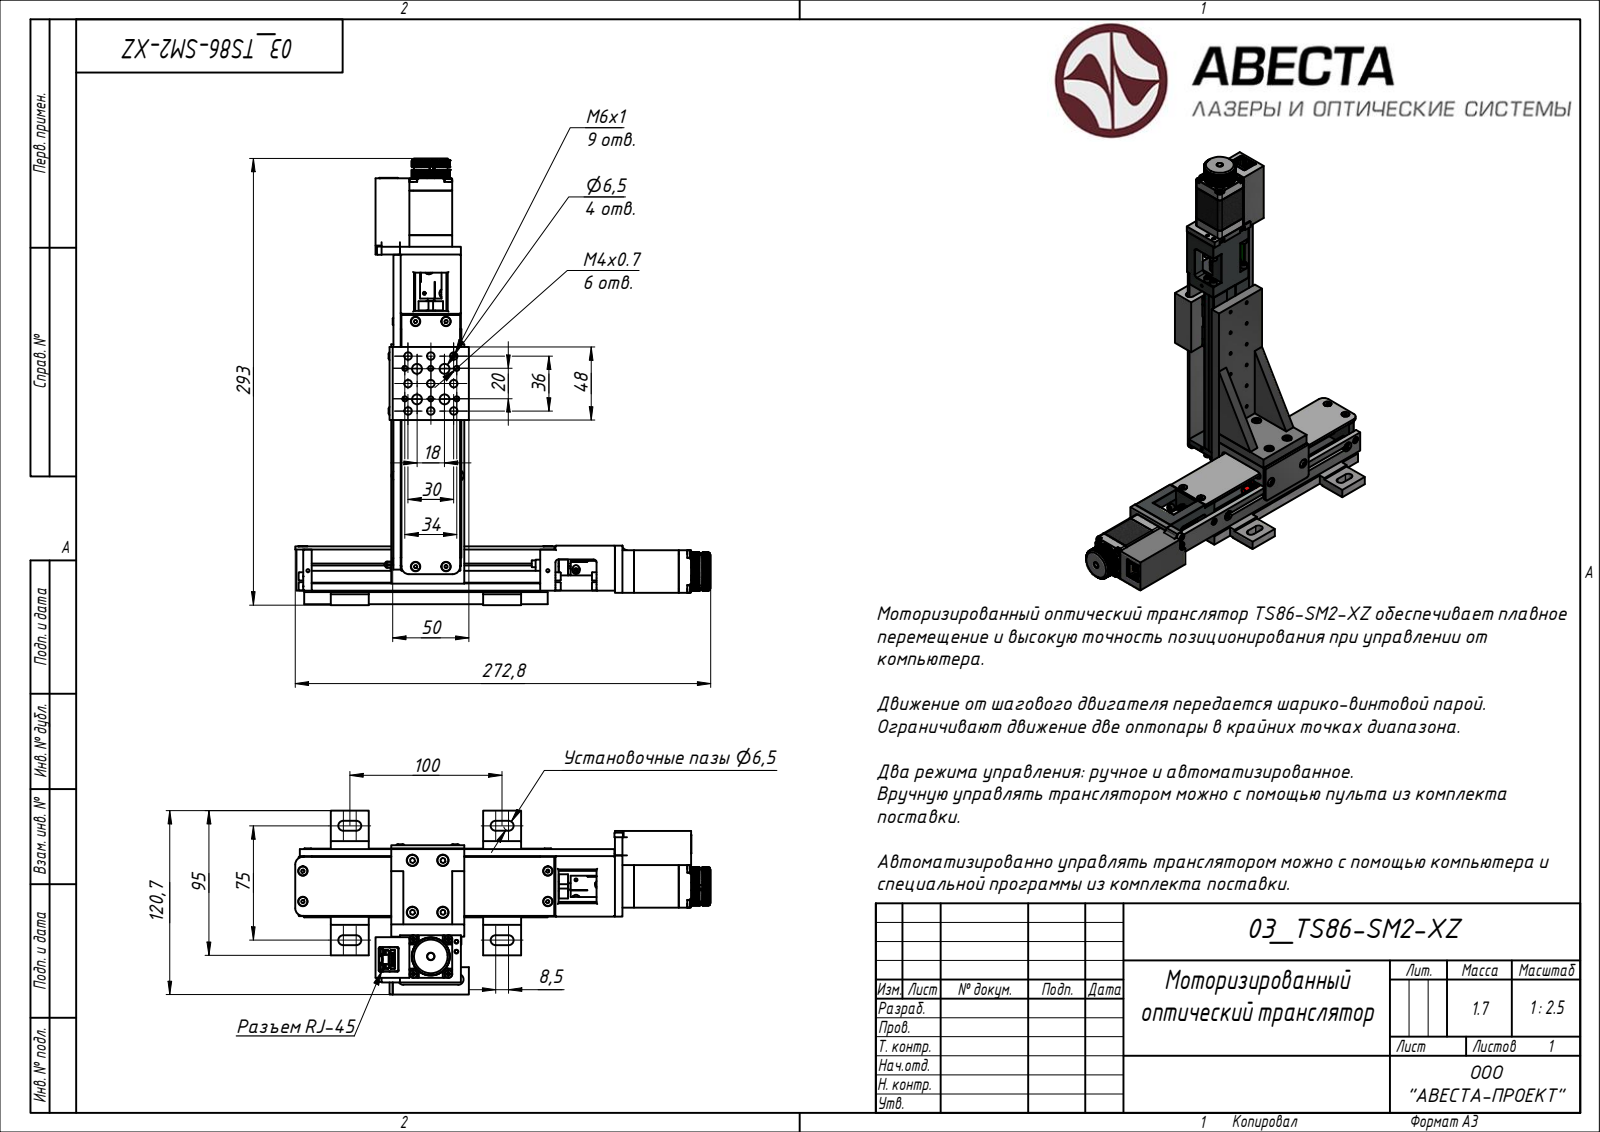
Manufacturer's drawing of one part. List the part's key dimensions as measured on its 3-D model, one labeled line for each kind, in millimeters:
STEP written by: Rhino 7.34 (AUTOMOTIVE_DESIGN)
Units: millimetres
Bodies: 1 solid, 4820 faces (2906 planar, 1326 cylindrical, 588 other)
Overall size (bounding box): 293 × 272.8 × 120.7
Volume: 601 438 mm³ · Surface area: 242 169 mm²
Round holes (diameter × count): ⌀3.4 ×28, ⌀6.5 ×20, ⌀2.46 ×17, ⌀3.24 ×15, ⌀7.5 ×15, ⌀2.5 ×14, ⌀1.05 ×10, ⌀4.92 ×10, ⌀2.46 ×9, ⌀5 ×8, ⌀2.15 ×6, ⌀4.92 ×6
Round bosses / shafts (diameter × count): ⌀4.5 ×20, ⌀5.5 ×12, ⌀6 ×10, ⌀5.3 ×8, ⌀3 ×8, ⌀2.5 ×8, ⌀7 ×6, ⌀5 ×6
Partial cylindrical surfaces — rounded edges, fillets, slot ends (radius × count): R0.5 ×72, R2.5 ×20, R3 ×20, R2 ×16, R1 ×8, R3.25 ×8, R1.75 ×4, R2.4 ×4
Main face-to-face distances: 2, 8, 0.5, 2.5, 7, 29.5, 4.5, 28, 5, 1.5
Hole centre spacings: 20, 26.91, 18, 60, 62.64, 40, 20.02, 43.86
